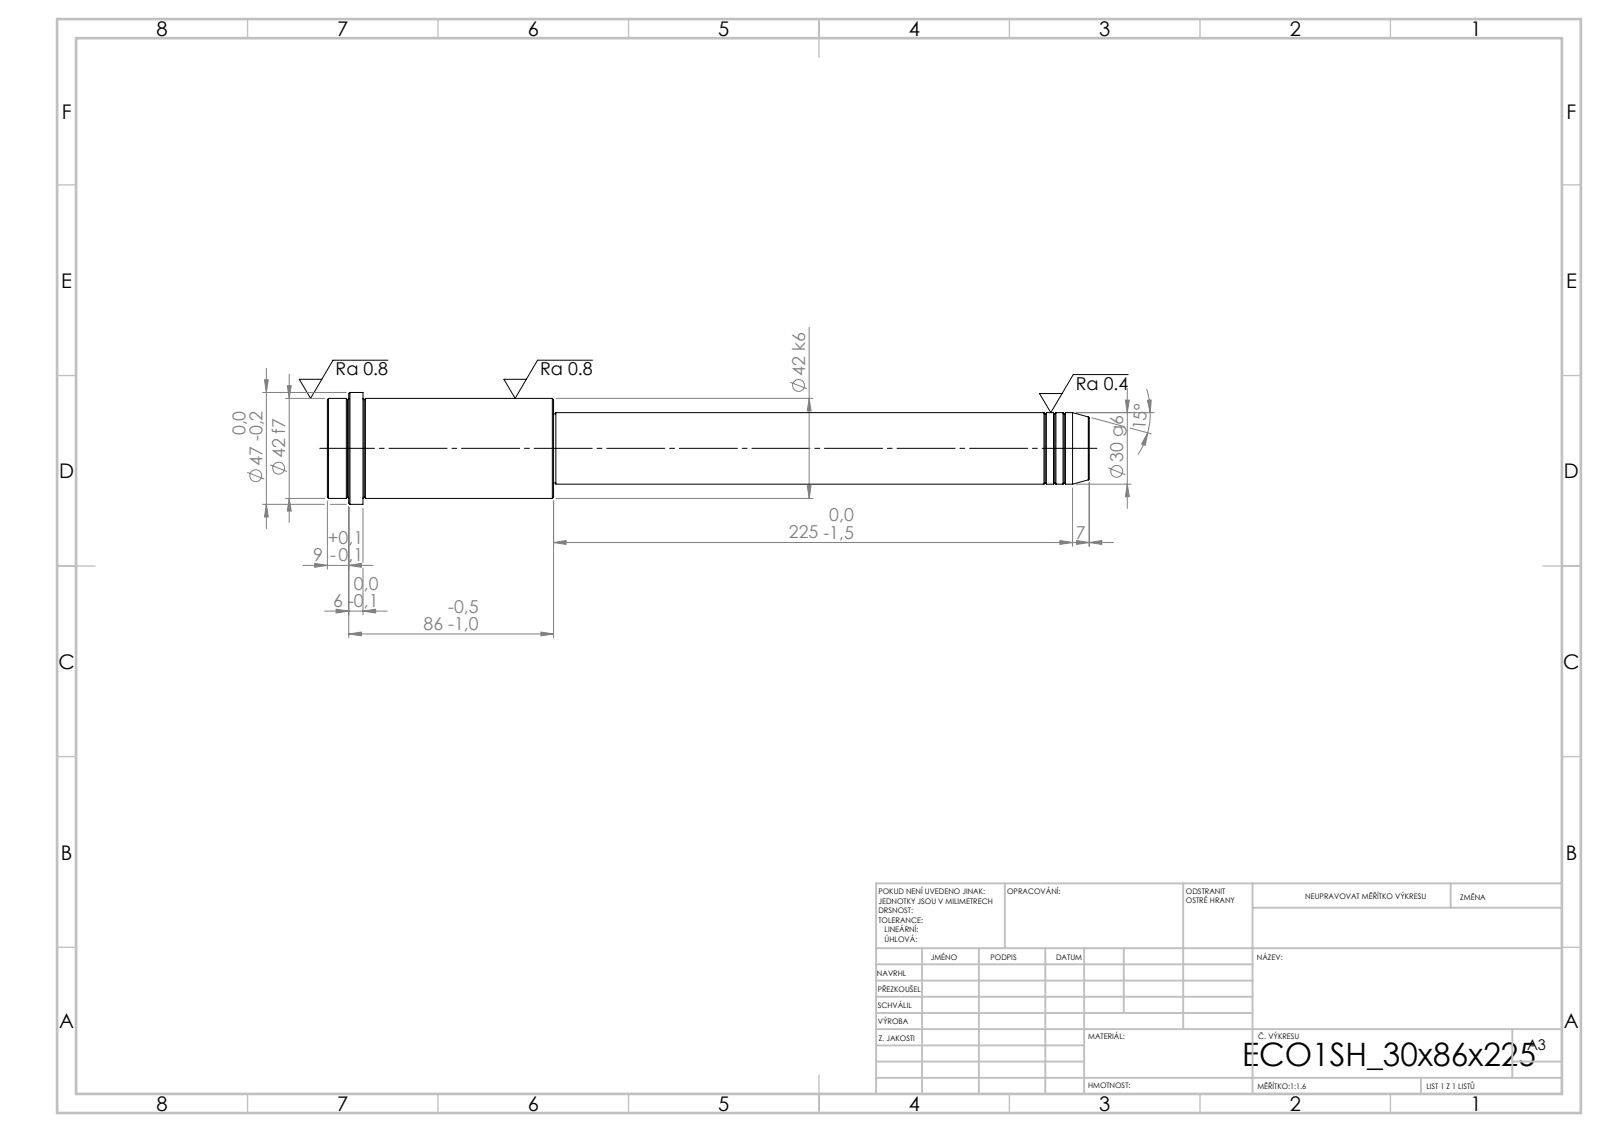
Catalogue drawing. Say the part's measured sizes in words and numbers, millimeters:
Its 3-D file was written by "SolidWorks 2019 (CONFIG_CONTROL_DESIGN)". It is 1 solid with 52 faces: 6 planar, 16 cylindrical and 30 other. Overall it measures 320 by 47 by 47 millimeters. Its volume is 291 852 cubic millimeters and its surface area 37 375 square millimeters. Round bosses or shafts: 1 of diameter 47, 1 of diameter 42, 1 of diameter 30, 1 of diameter 29. The main face-to-face distances are 95, 225, 320, 305, 80, 15, 311, 86, 6, 9.
